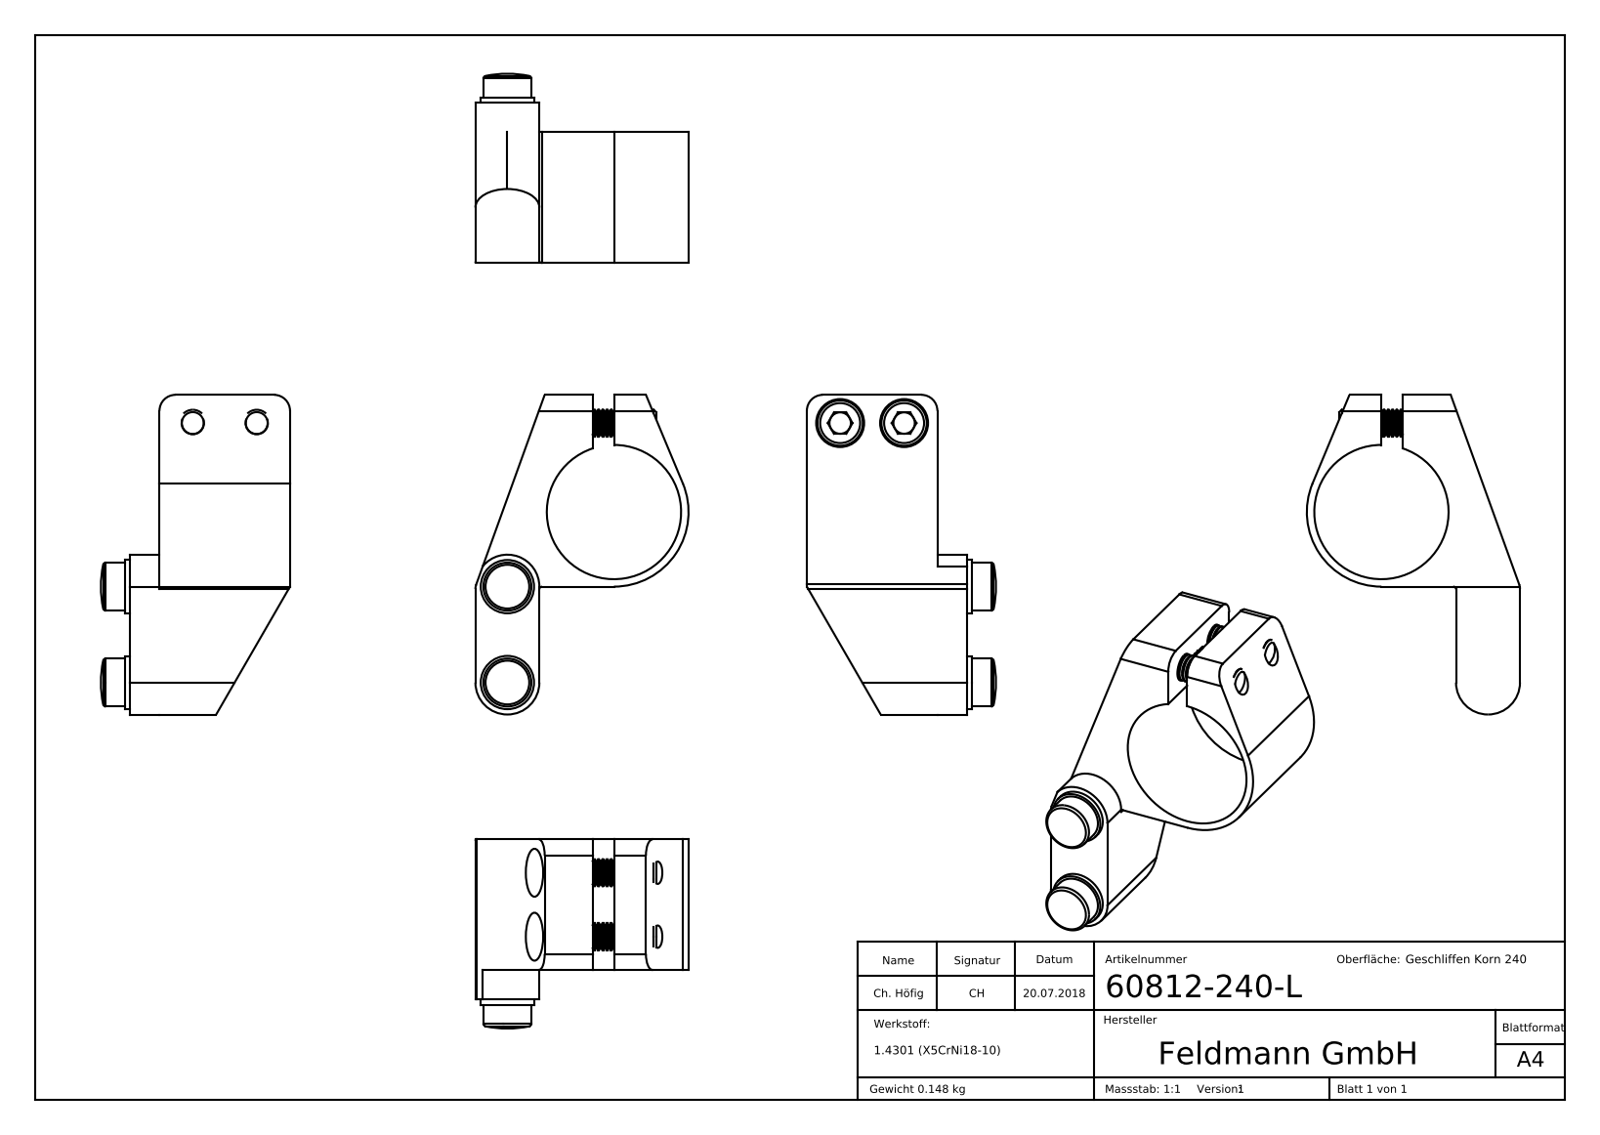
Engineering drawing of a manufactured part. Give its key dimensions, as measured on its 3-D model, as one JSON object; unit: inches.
{"part_name": "socket head cap screw_din_DIN 912 M5 x 16 --- 16S; 60812-240-X Teil2_60812-240-X Teil2; 60812-240-X Teil1_60812-240-L Teil1; 60812-240-L", "step_written_by": "SolidWorks 2015 (CONFIG_CONTROL_DESIGN)", "units": "inches", "bodies": {"solids": 5, "faces": 575, "planar": 183, "cylindrical": 116, "other": 276}, "overall_size": [2.362, 1.575, 1.398], "volume_in3": 1.246, "surface_area_in2": 16.98, "round_holes": [[0.165, 2], [0.197, 2], [0.205, 2], [0.354, 2], [0.992, 1]], "round_bosses_or_shafts": [[0.394, 2], [0.354, 2], [0.335, 2], [0.197, 2]], "partial_cylinders_radius": [[0.118, 2], [0.236, 2], [0.02, 1], [0.098, 1], [0.551, 1]], "face_to_face_distances": [0.965, 0.472, 1.181, 0.217, 1.417, 0.394, 0.866, 1.024, 0.551, 0.157], "hole_center_spacings": [0.472, 0.709, 0.961, 1.486]}
